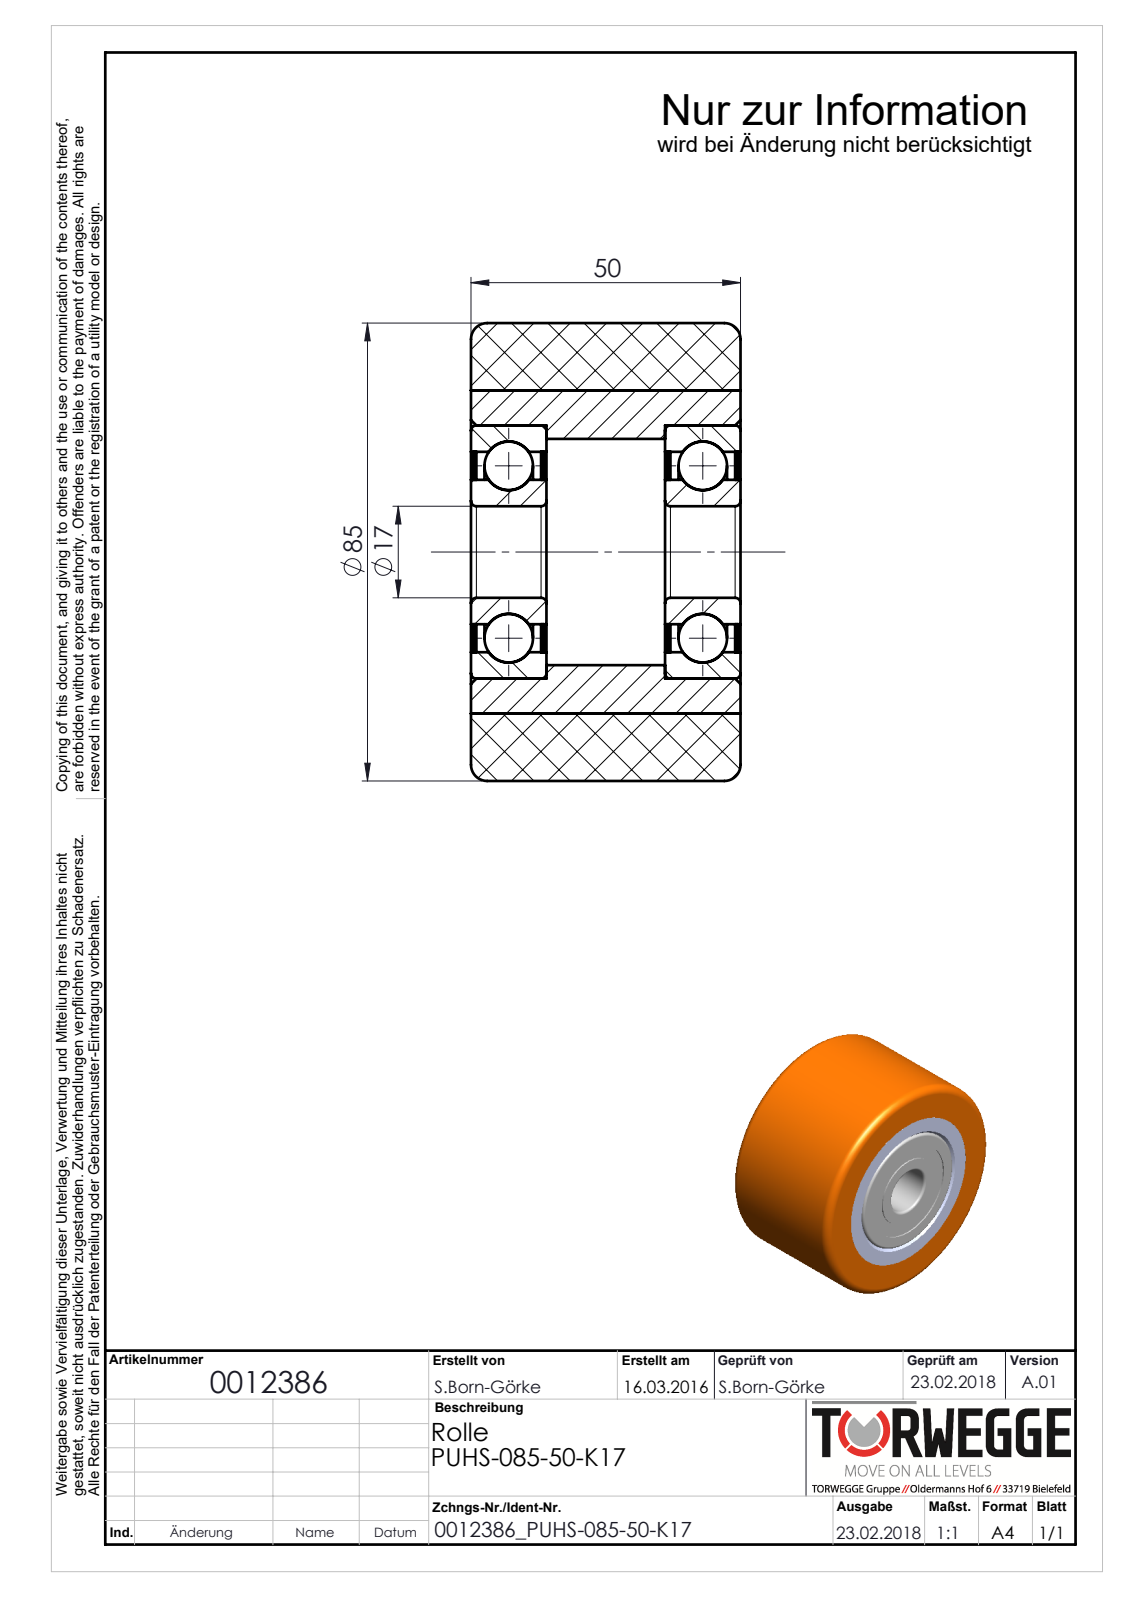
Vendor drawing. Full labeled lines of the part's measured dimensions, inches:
Part name (STEP PRODUCT): 0012386_PUHS-085-50-K17
STEP written by: SolidWorks 2016 (AUTOMOTIVE_DESIGN)
Units: inches
Bodies: 12 solids, 118 faces (22 planar, 52 cylindrical, 44 other)
Overall size (bounding box): 3.346 × 3.346 × 1.969
Volume: 14.67 in³ · Surface area: 112.5 in²
Round holes (diameter × count): ⌀0.669 ×1, ⌀1.055 ×1, ⌀1.465 ×1, ⌀1.654 ×1, ⌀1.85 ×1, ⌀2.362 ×1
Round bosses / shafts (diameter × count): ⌀3.346 ×1
Main face-to-face distances: 1.417, 0.02, 1.969, 0.512, 0.551, 0.039, 0.531, 1.437, 0.492, 1.398
